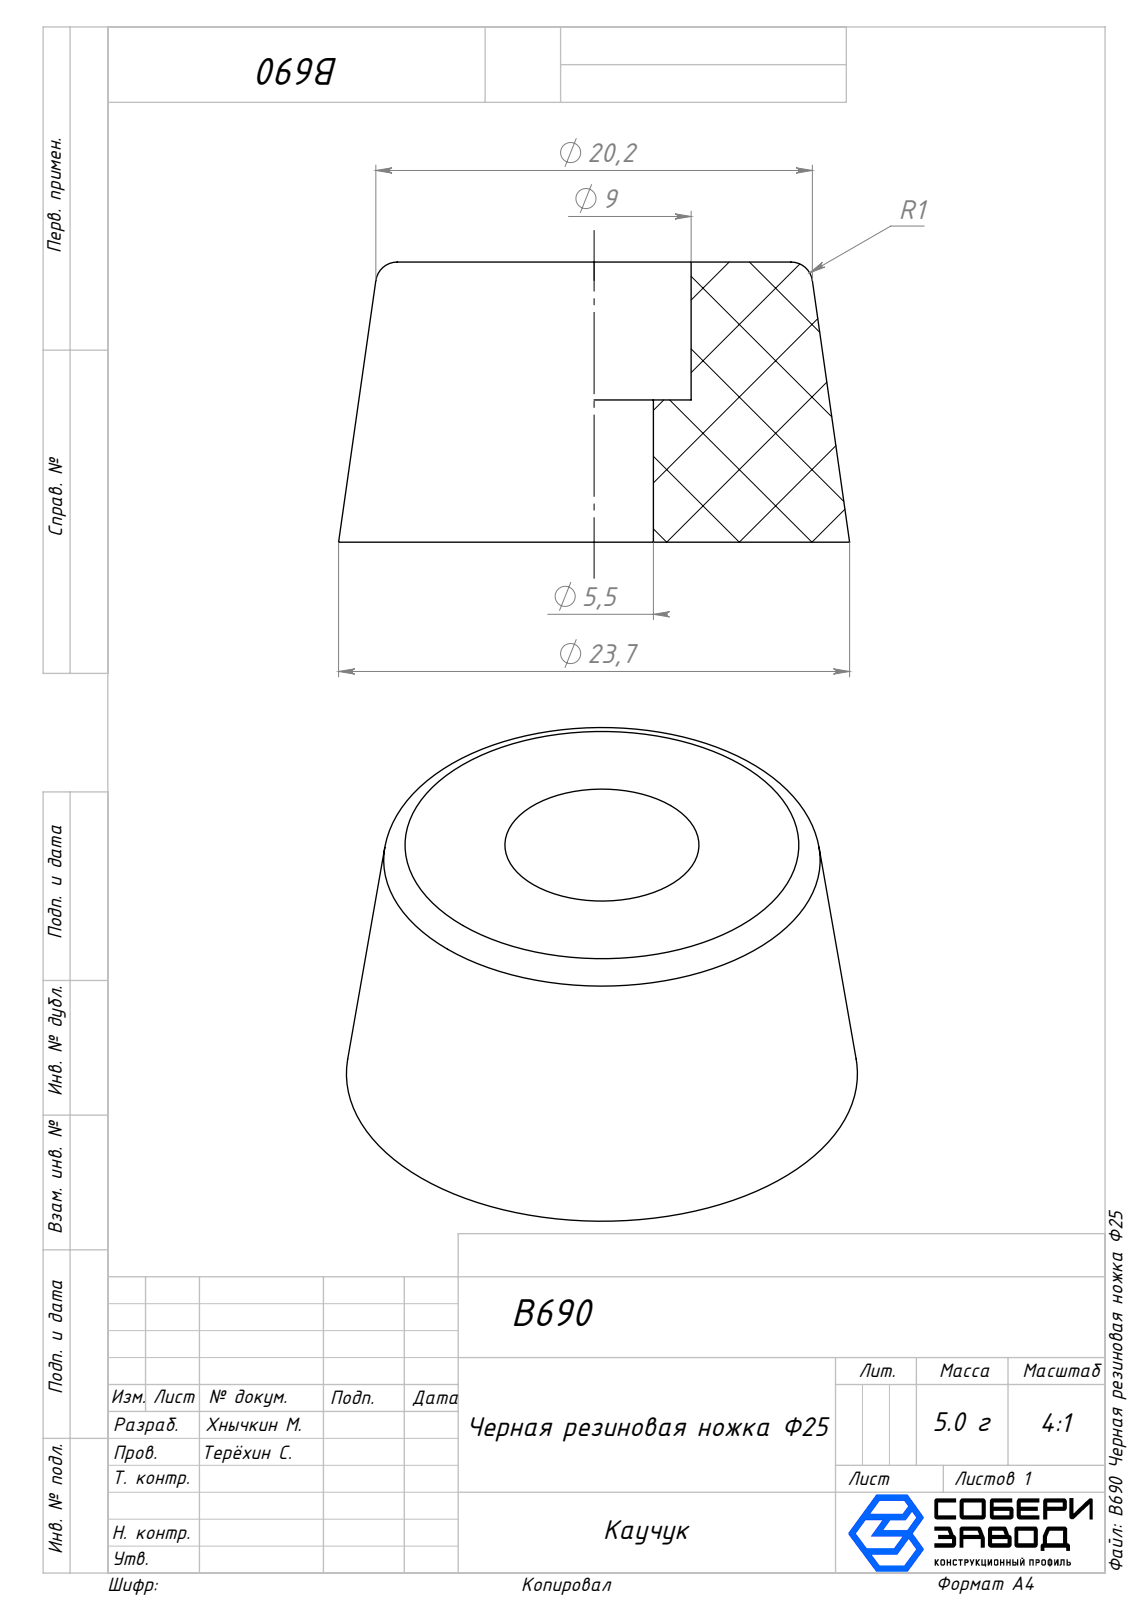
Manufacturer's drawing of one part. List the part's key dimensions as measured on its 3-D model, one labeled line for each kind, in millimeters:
Part name (STEP PRODUCT): B690 Черная резиновая ножка Ф25
STEP written by: SolidWorks 2025 (AUTOMOTIVE_DESIGN)
Units: millimetres
Bodies: 1 solid, 9 faces (3 planar, 4 cylindrical, 2 other)
Overall size (bounding box): 23.7 × 23.7 × 13
Volume: 4 322 mm³ · Surface area: 1 904 mm²
Round holes (diameter × count): ⌀5.5 ×1, ⌀9 ×1
Main face-to-face distances: 13, 6.6, 6.4
